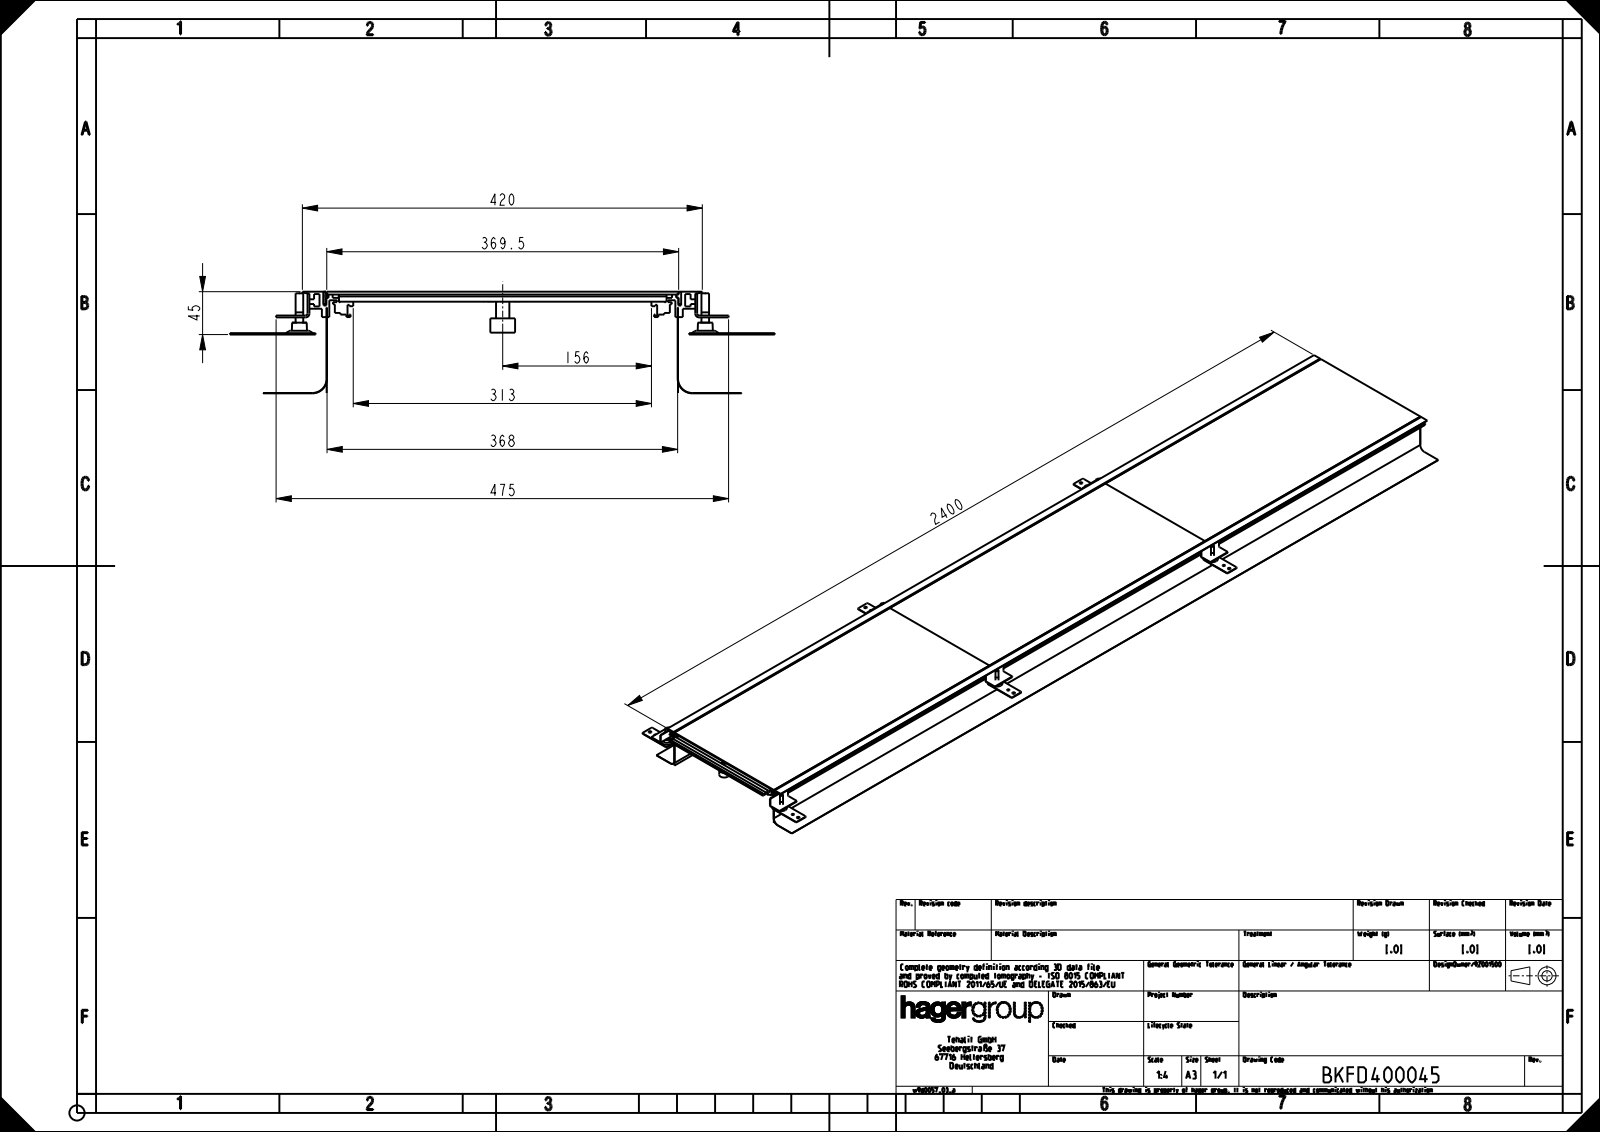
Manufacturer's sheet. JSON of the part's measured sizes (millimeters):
{"part_name": "U05644KUN; U05650KUN; U05994KUN; U05647KUN (+8 more)", "step_written_by": "CREO PARAMETRIC BY PTC INC, 2020281 (AUTOMOTIVE_DESIGN)", "units": "millimeters", "bodies": {"solids": 62, "faces": 1026, "planar": 600, "cylindrical": 354, "other": 72}, "overall_size": [2432.5, 572.13, 106.7], "volume_mm3": 6952000, "surface_area_mm2": 5457000, "round_holes": [[7, 15], [8, 9], [10, 9], [6, 6], [8.5, 6], [11.5, 6], [17.5, 6], [23, 6]], "round_bosses_or_shafts": [[26, 9], [14, 9], [11.9, 9], [20, 6], [8, 6]], "partial_cylinders_radius": [[2, 92], [3, 24], [0.5, 20], [4, 2], [15, 2], [15.4, 2]], "face_to_face_distances": [3, 0.4, 368.55, 103.7, 106.7, 103.3, 106.3, 6.5, 7.5, 4], "hole_center_spacings": [800, 1600, 800.25, 801.1, 802.4, 926.9, 937.16, 959.71]}
